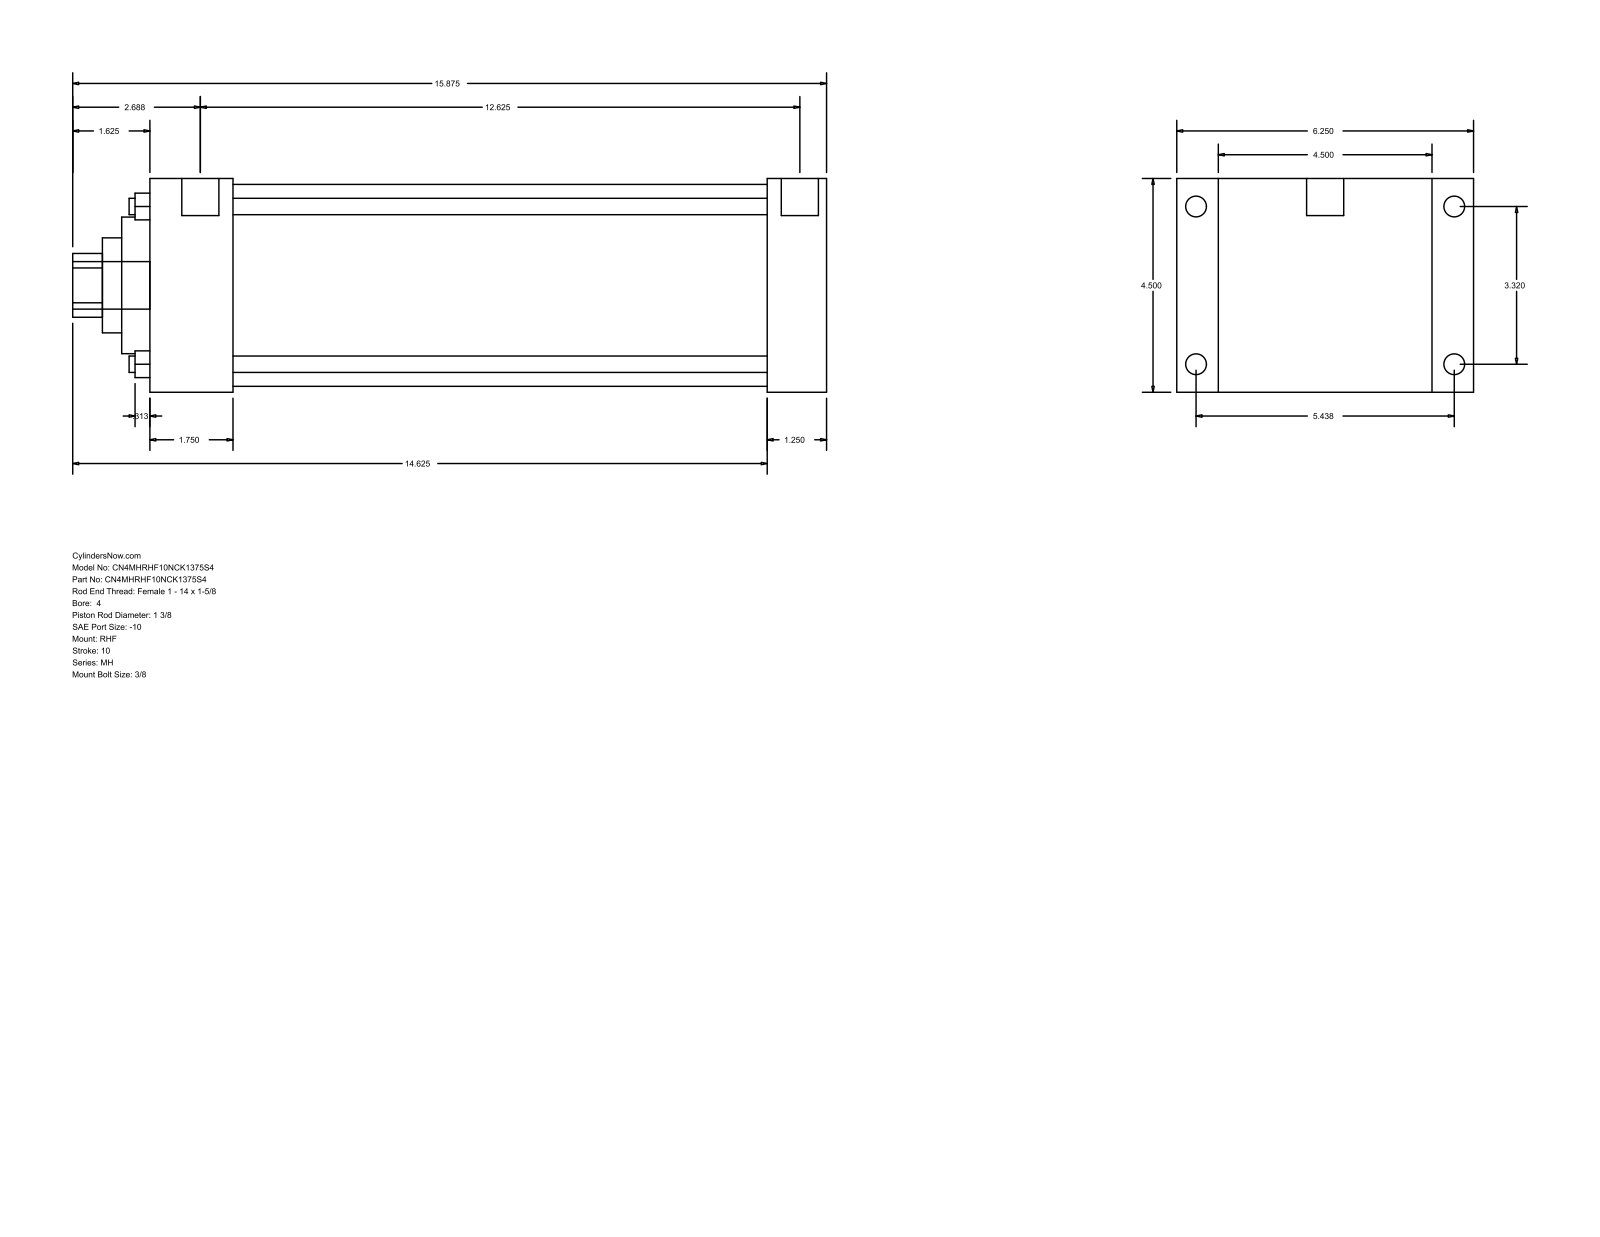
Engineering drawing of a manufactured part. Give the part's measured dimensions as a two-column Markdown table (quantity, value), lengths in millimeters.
| quantity | value |
| --- | --- |
| part name | MH_RHF__0400_1.375 |
| STEP written by | GSSL Pune (CONFIG_CONTROL_DESIGN) |
| units | millimeters |
| bodies | 0 solids, 90 faces (61 planar, 29 cylindrical, 0 other) |
| overall size | 403.23 × 158.75 × 114.3 |
| round holes (diameter × count) | 8.76 × 4, 34.92 × 1, 50.8 × 1, 73.03 × 1, 107.95 × 1 |
| round bosses / shafts (diameter × count) | 11.13 × 4, 8.73 × 4, 19.84 × 2, 25.4 × 1 |
| partial cylindrical surfaces (radius × count) | 17.06 × 1 |
| main face-to-face distances | 114.3, 361.96, 330.21, 31.75, 22.23, 136.53, 44.45, 285.76, 317.51, 158.76 |
| hole center spacings | 59.62, 84.32, 119.25 |
